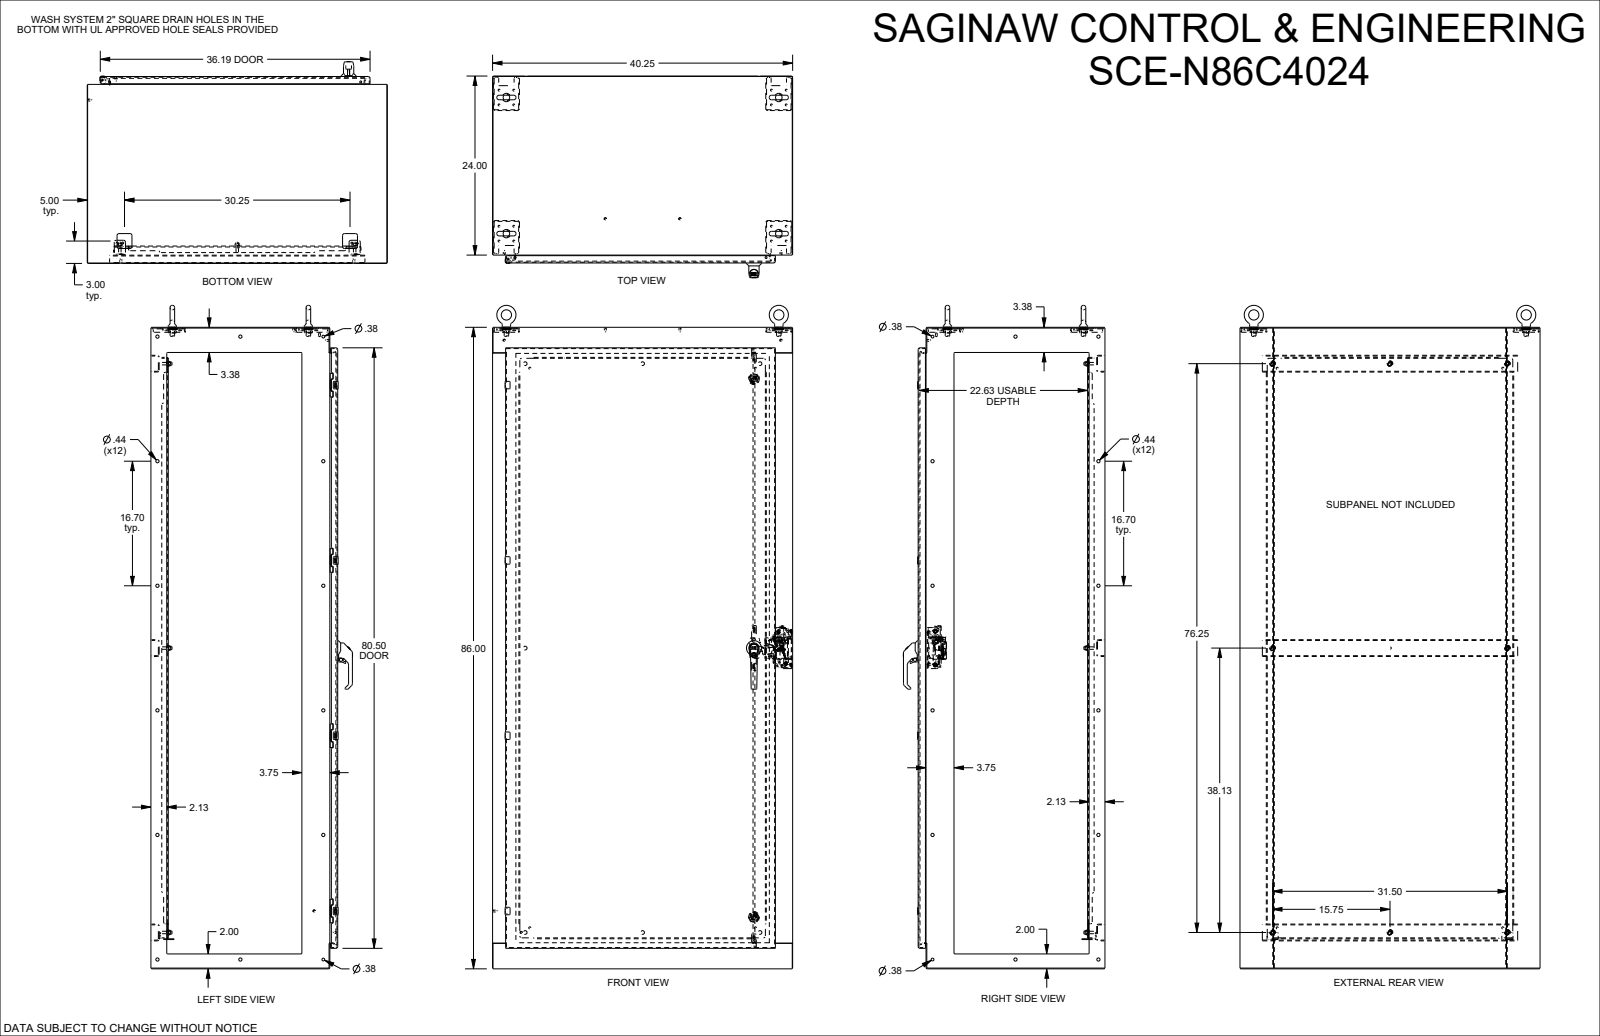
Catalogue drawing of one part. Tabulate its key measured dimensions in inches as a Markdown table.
| quantity | value |
| --- | --- |
| part name | SCE-N86C4024 |
| STEP written by | SolidWorks 2023 (AUTOMOTIVE_DESIGN) |
| units | inches |
| bodies | 31 solids, 4204 faces (1650 planar, 1476 cylindrical, 1078 other) |
| overall size | 88.945 × 40.25 × 27.046 |
| volume | 1 212 in³ |
| surface area | 22 902 in² |
| round holes (diameter × count) | 0.25 × 18, 0.437 × 12, 0.375 × 10, 0.205 × 8, 0.244 × 8, 0.04 × 4, 0.17 × 4, 0.218 × 4, 0.256 × 4, 0.875 × 4, 0.135 × 2, 0.156 × 2 |
| round bosses / shafts (diameter × count) | 0.17 × 12, 0.25 × 11, 0.24 × 8, 0.196 × 5, 1.173 × 4, 0.6 × 4, 1.4 × 2, 0.48 × 2 |
| partial cylindrical surfaces (radius × count) | 0.03 × 126, 0.015 × 108, 0.125 × 87, 0.063 × 43, 0.02 × 38, 0.167 × 38, 0.229 × 32, 0.25 × 27 |
| main face-to-face distances | 0.104, 24.954, 25.058, 24.85, 85.896, 23.896, 1.058, 0.104, 40.146, 85.792 |
| hole center spacings | 1.979, 1.4, 23.5, 16.7, 27.82, 2.799, 17.289, 18.25 |
